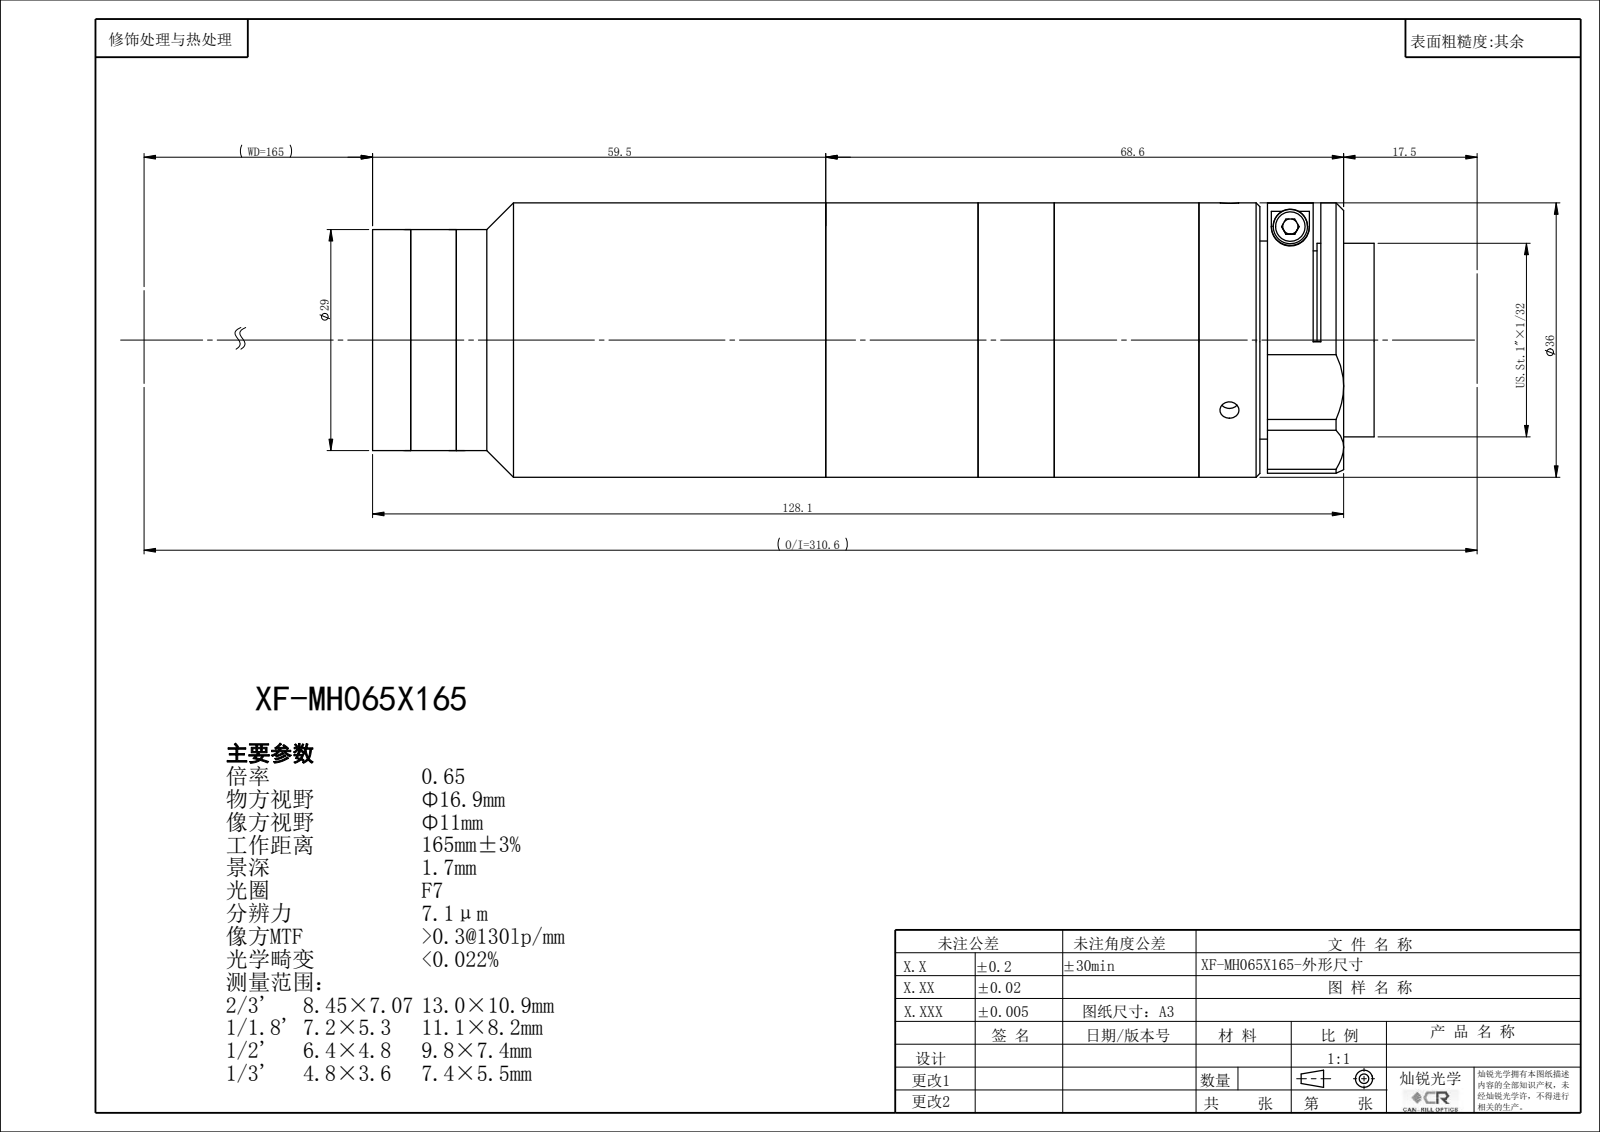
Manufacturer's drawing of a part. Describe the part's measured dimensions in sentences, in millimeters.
The part is named "XF-MH065X165". Its 3-D file was written by "SolidWorks 2022 (CONFIG_CONTROL_DESIGN)". It is 0 solids with 125 faces: 59 planar, 44 cylindrical and 22 other. Overall it measures 132.07 by 36 by 36 millimeters. Round holes: 3 of diameter 2.5, 1 of diameter 18, 1 of diameter 22.4, 1 of diameter 24, 1 of diameter 24.9, 1 of diameter 26.4. Round bosses or shafts: 1 of diameter 36, 1 of diameter 34, 1 of diameter 29, 1 of diameter 25.4. The main face-to-face distances are 19.57, 56, 1.5, 18.07, 19, 37.07, 38.57, 20, 30, 49.
